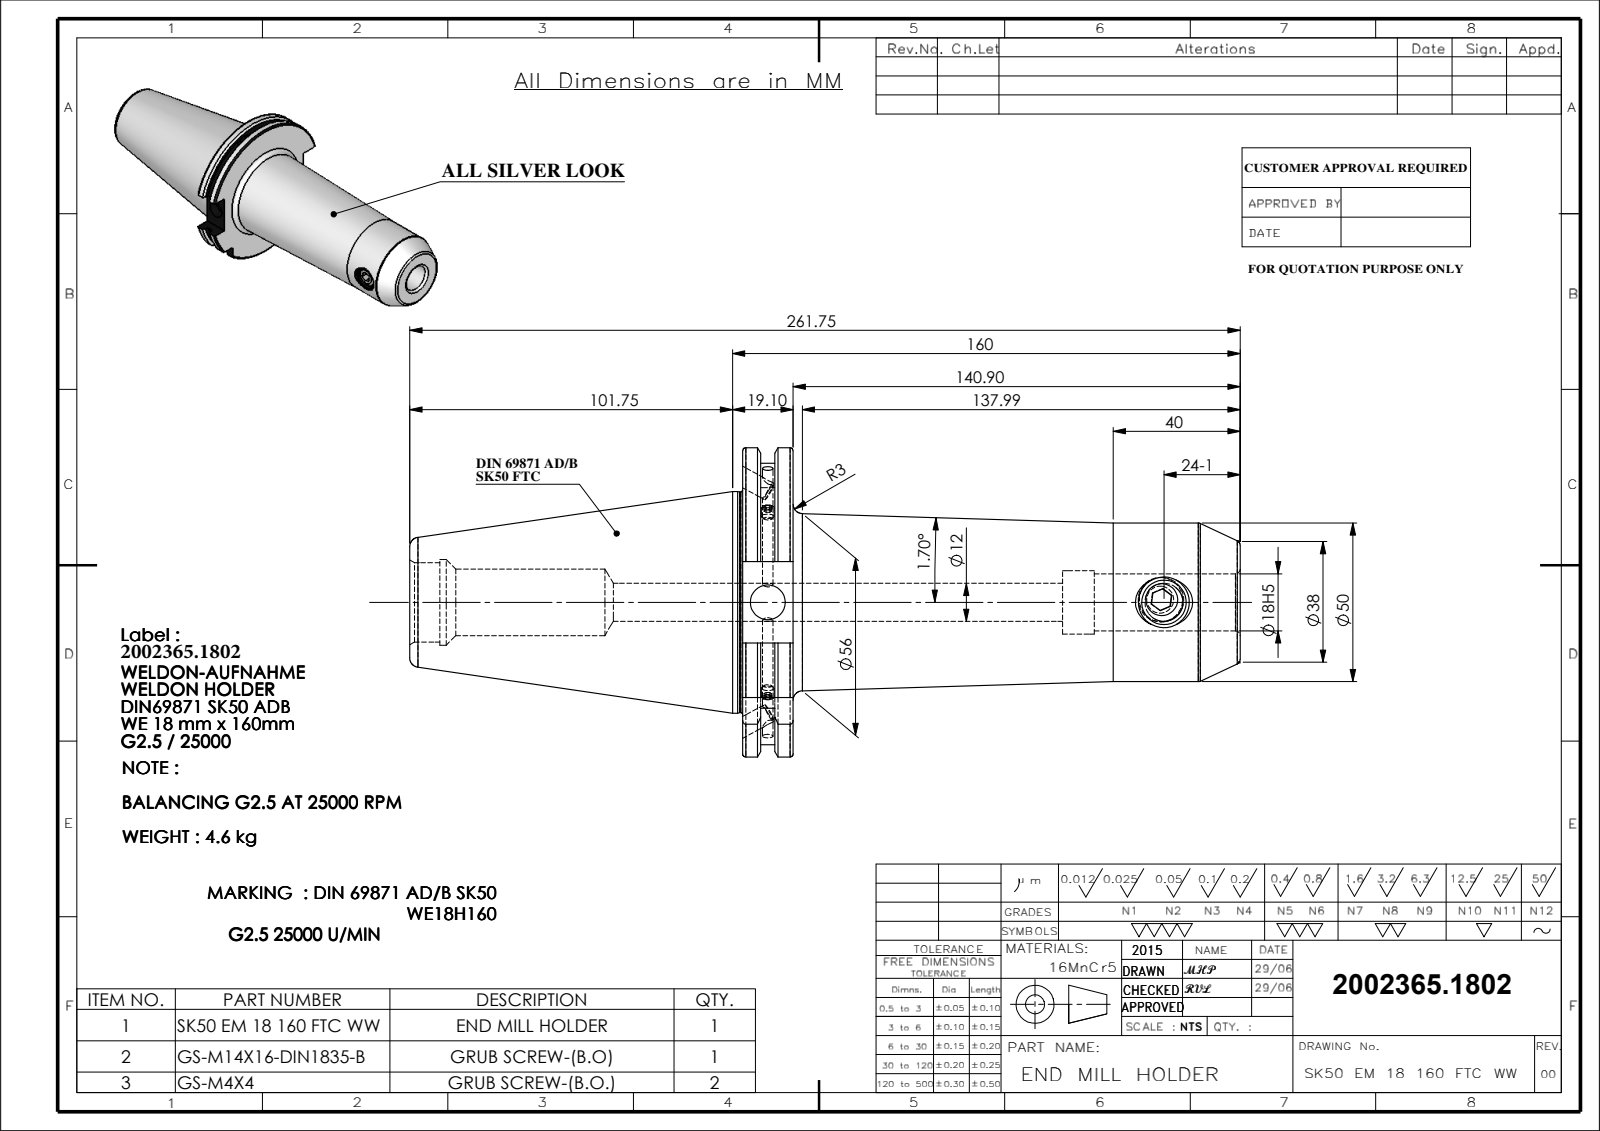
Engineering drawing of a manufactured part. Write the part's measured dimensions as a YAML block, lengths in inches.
part_name: "SK50 EM 18 160 FTC WW; M14X16_ISO 4026 - M12 x 12-N; 91506-WE718160; M4X4_DIN 913 - M4 x 4-N"
step_written_by: "SolidWorks 2009 (CONFIG_CONTROL_DESIGN)"
units: inches
bodies: {solids: 4, faces: 170, planar: 53, cylindrical: 55, other: 62}
overall_size: [10.305, 3.839, 3.703]
volume: 36.77
surface_area: 113.6
round_holes:
  - {diameter: 0.236, count: 2}
  - {diameter: 0.472, count: 2}
  - {diameter: 0.13, count: 1}
  - {diameter: 0.433, count: 1}
  - {diameter: 0.63, count: 1}
  - {diameter: 0.709, count: 1}
  - {diameter: 0.787, count: 1}
  - {diameter: 0.827, count: 1}
  - {diameter: 0.984, count: 1}
  - {diameter: 1.063, count: 1}
round_bosses_or_shafts:
  - {diameter: 0.157, count: 2}
  - {diameter: 2.75, count: 1}
  - {diameter: 2.734, count: 1}
  - {diameter: 1.969, count: 1}
  - {diameter: 0.551, count: 1}
partial_cylinders:
  - {radius: 1.768, count: 1}
  - {radius: 1.919, count: 1}
face_to_face_distances: [0.626, 6.173, 5.547, 0.223, 0.403, 5.95, 0.4, 0.177, 0.226, 5.774]
hole_center_spacings: [4.917]
